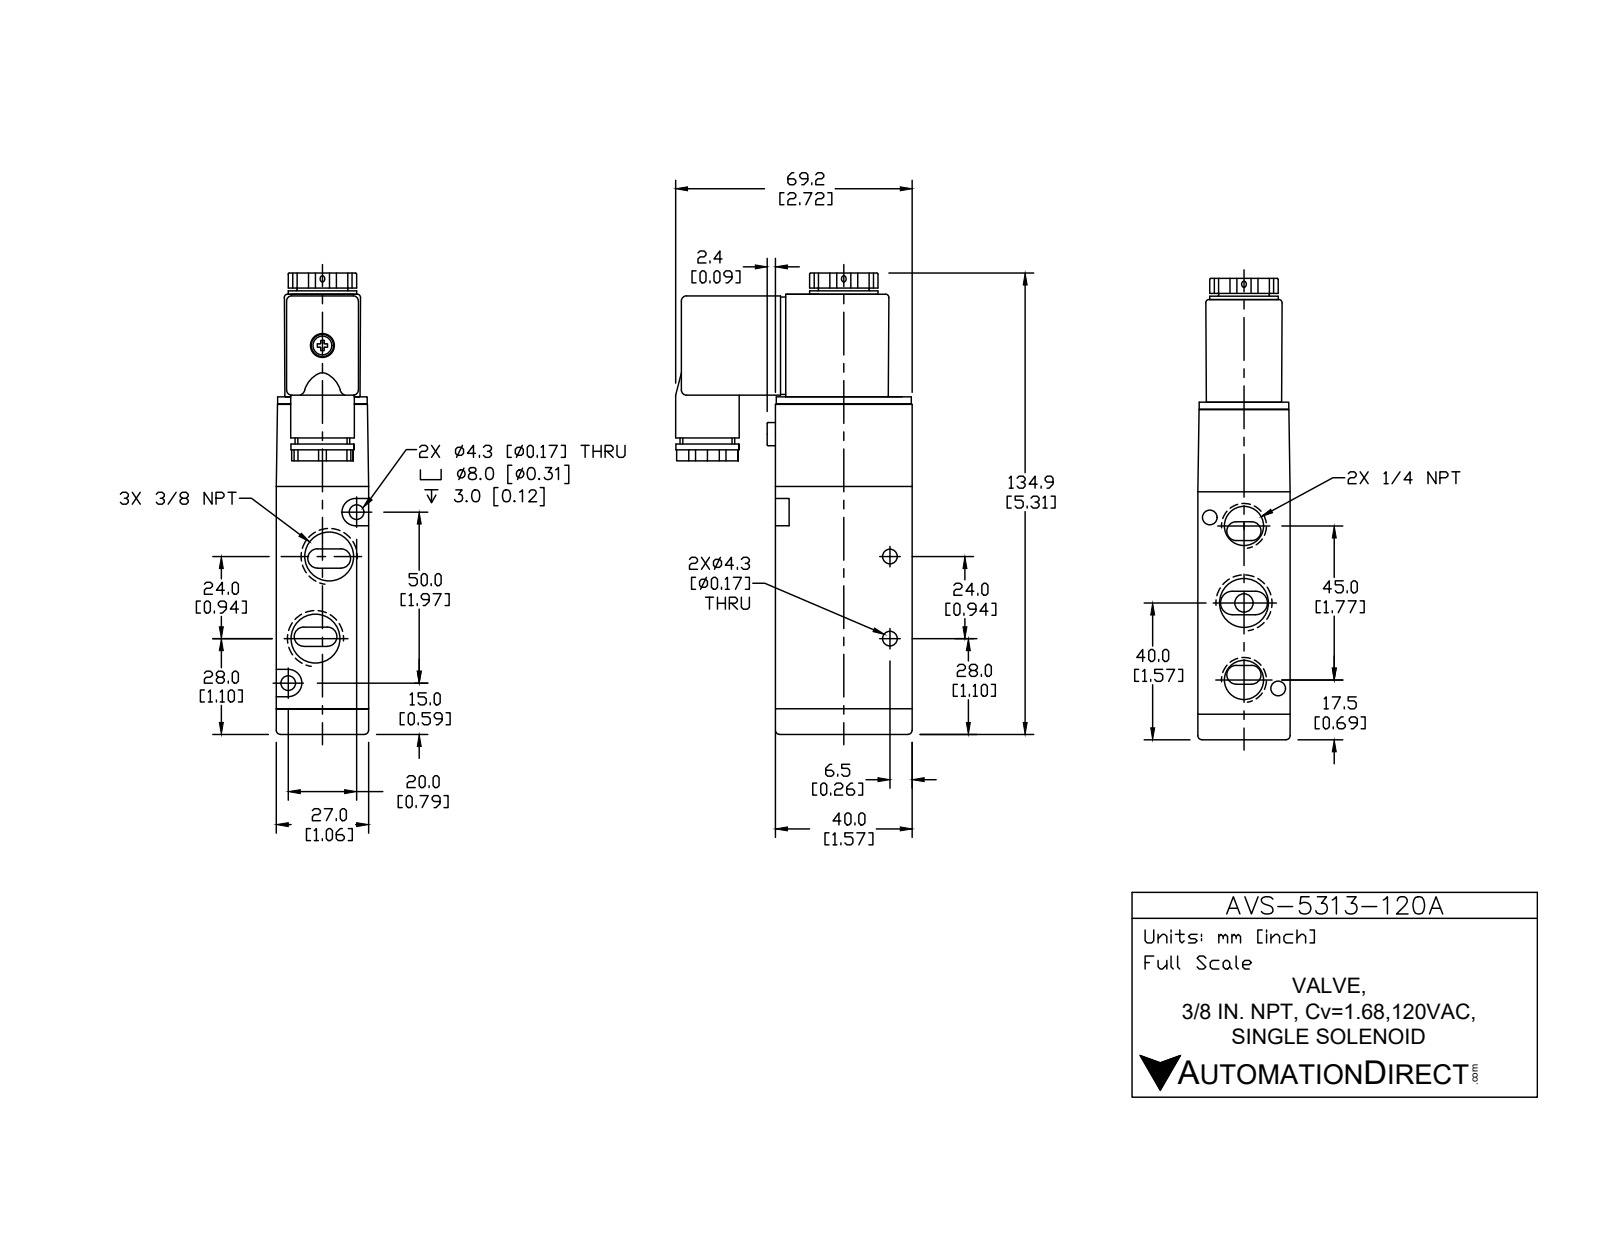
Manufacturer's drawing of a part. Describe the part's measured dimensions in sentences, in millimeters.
The part is named "AVS-5313-120A". Its 3-D file was written by "SolidWorks 2015 (CONFIG_CONTROL_DESIGN)". It is 4 solids with 192 faces: 88 planar, 77 cylindrical and 27 other. Overall it measures 134.9 by 69.2 by 27 millimeters. Its volume is 137 713 cubic millimeters and its surface area 32 379 square millimeters. Round holes: 4 of diameter 4.3, 3 of diameter 14.27, 2 of diameter 11.13, 1 of diameter 9.3. Round bosses or shafts: 1 of diameter 20, 1 of diameter 18.6, 1 of diameter 18.4, 1 of diameter 16, 1 of diameter 14.8, 1 of diameter 6.7. Partial cylindrical surfaces (rounded edges, fillets, slot ends): 12 of radius 1.5, 12 of radius 3, 8 of radius 0.5, 5 of radius 1. The main face-to-face distances are 27, 65, 40, 24, 3, 7.5, 72.5, 29.5, 21, 27.5. The hole center spacings are 10.31, 10.69, 12.17, 15.26, 22.5, 26.93, 34.56, 38.9.
